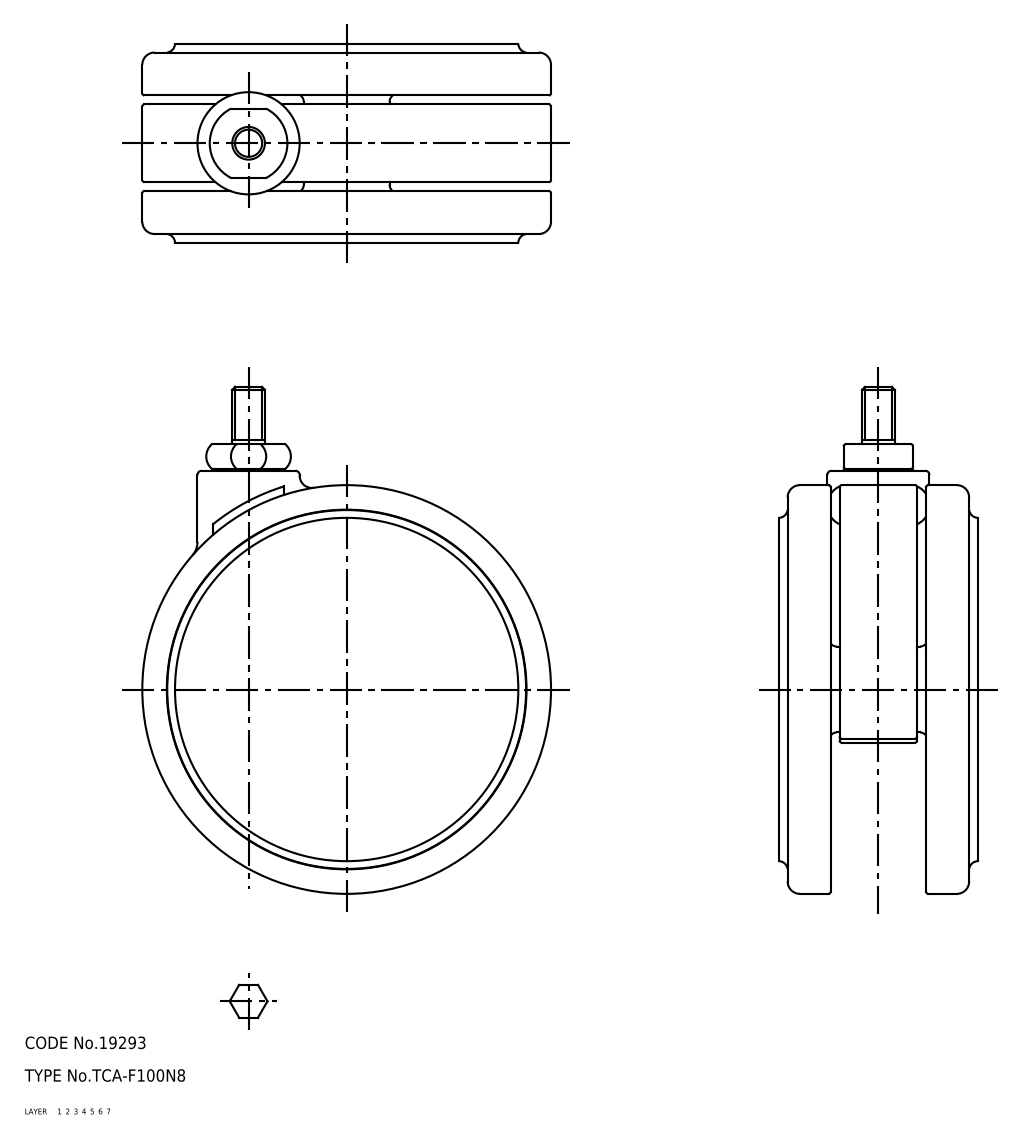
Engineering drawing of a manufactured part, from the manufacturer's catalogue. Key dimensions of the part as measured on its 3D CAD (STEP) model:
Part name (STEP PRODUCT): caster; TCA-F100N8
STEP written by: SolidWorks 2015 (AUTOMOTIVE_DESIGN)
Units: millimetres
Bodies: 1 solid, 999 faces (379 planar, 396 cylindrical, 224 other)
Overall size (bounding box): 124 × 100 × 48.6
Volume: 176 151 mm³ · Surface area: 88 890 mm²
Round holes (diameter × count): ⌀7.98 ×1, ⌀8.07 ×1, ⌀9.3 ×1, ⌀10.7 ×1, ⌀12.3 ×1, ⌀13 ×1, ⌀24 ×1, ⌀81 ×1, ⌀88 ×1
Round bosses / shafts (diameter × count): ⌀100 ×1, ⌀87.8 ×1, ⌀25 ×1, ⌀22 ×1, ⌀17 ×1, ⌀10.5 ×1, ⌀8 ×1, ⌀6.5 ×1
Partial cylindrical surfaces — rounded edges, fillets, slot ends (radius × count): R1 ×30, R0.5 ×19, R0.2 ×16, R2 ×10, R1.5 ×9, R3 ×6, R4 ×1, R8 ×1
Main face-to-face distances: 1.8, 45, 46.8, 3.6, 43.2, 7.6, 12.6, 9, 10.8, 36
